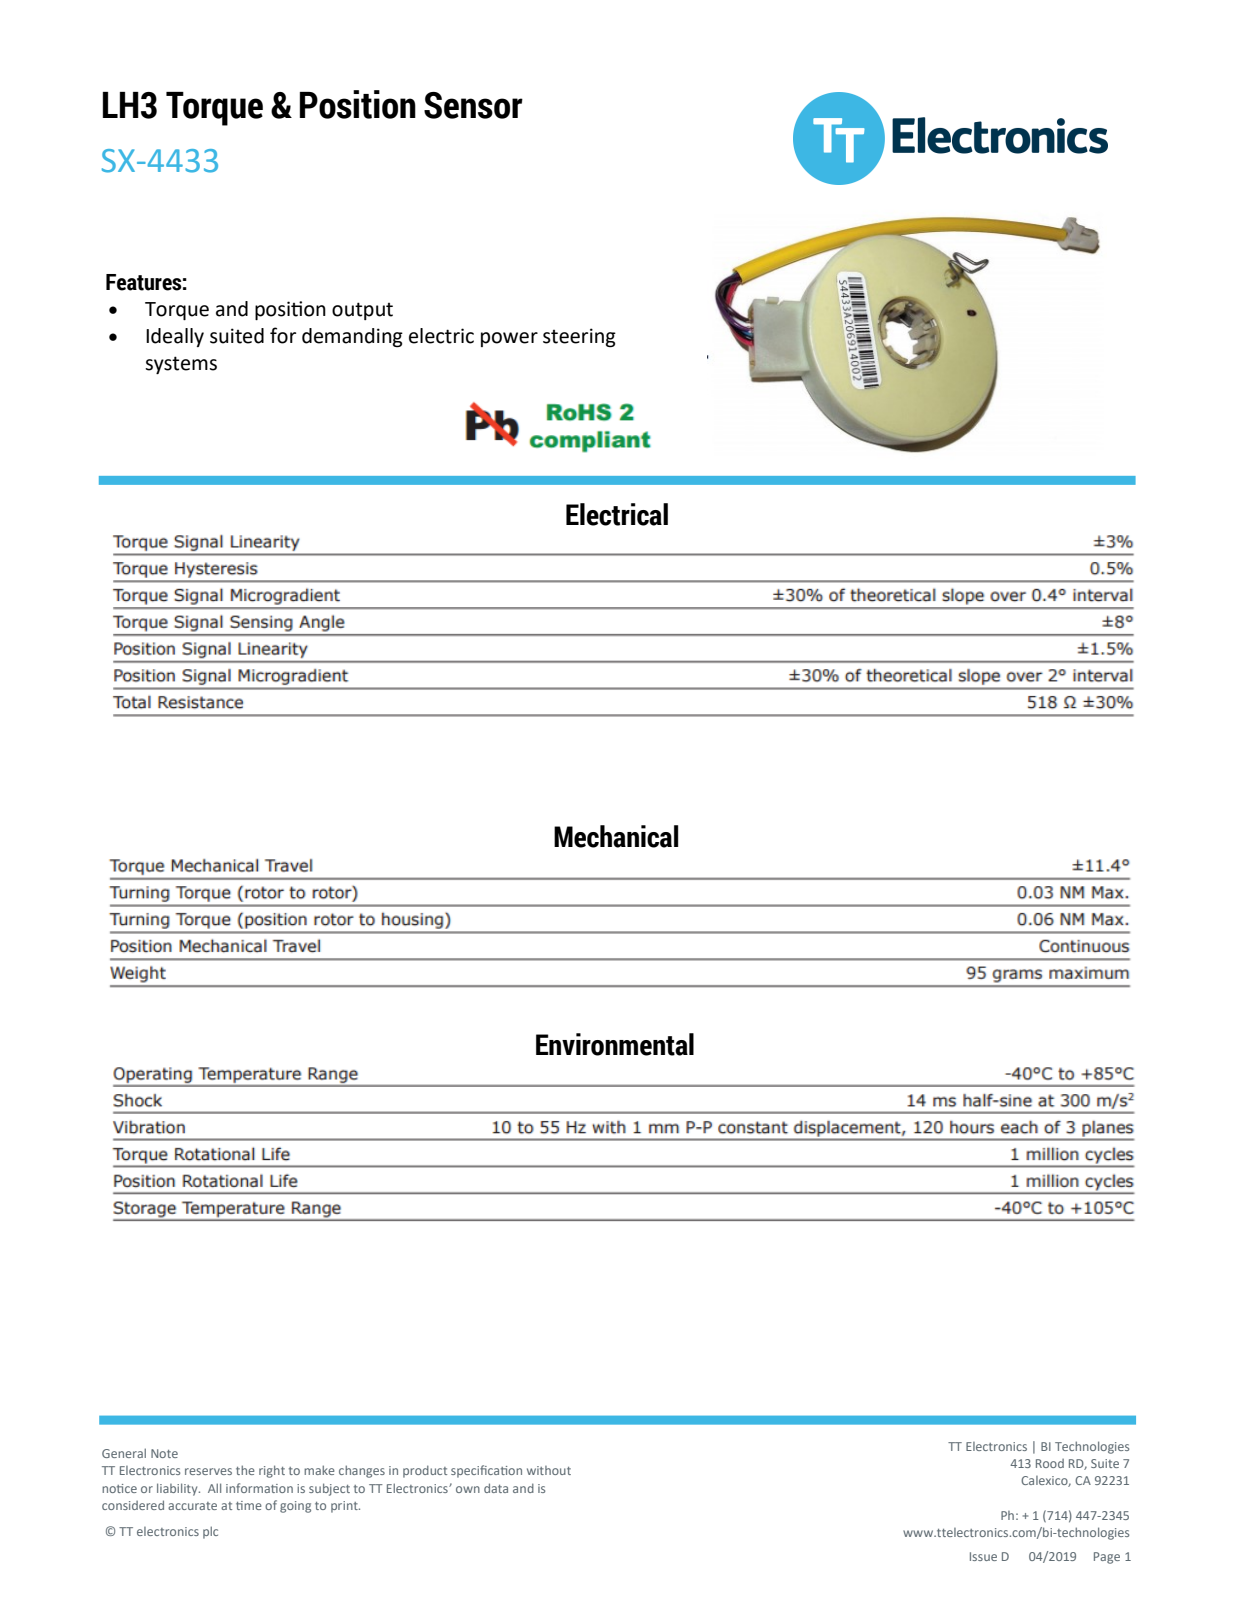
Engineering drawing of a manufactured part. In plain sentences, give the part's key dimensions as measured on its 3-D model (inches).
The part is named "SX-4433A_SW0001". Its 3-D file was written by "PRO/ENGINEER BY PARAMETRIC TECHNOLOGY CORPORATION, 2011490 (CONFIG_CONTROL_DESIGN)". It is 14 solids with 1854 faces: 855 planar, 660 cylindrical and 339 other. Overall it measures 8.597 by 3.2 by 1.728 inches. Its volume is 5.393 cubic inches and its surface area 49.76 square inches. Round holes: 6 of diameter 0.042, 4 of diameter 0.039, 1 of diameter 0.049, 1 of diameter 0.29, 1 of diameter 0.985, 1 of diameter 1.046, 1 of diameter 1.126, 1 of diameter 1.146, 1 of diameter 1.2, 1 of diameter 1.255, 1 of diameter 3.15. Round bosses or shafts: 23 of diameter 0.04, 6 of diameter 0.047, 1 of diameter 3.2, 1 of diameter 3.142, 1 of diameter 3.1, 1 of diameter 3.056, 1 of diameter 1.345, 1 of diameter 1.234. Partial cylindrical surfaces (rounded edges, fillets, slot ends): 72 of radius 0.007, 72 of radius 0.012, 63 of radius 0.01, 44 of radius 0.005, 32 of radius 0.01, 21 of radius 0.02, 19 of radius 0.016, 18 of radius 0.006. The main face-to-face distances are 0.719, 0.087, 0.521, 0.108, 0.012, 0.065, 0.729, 0.531, 0.11, 0.173. The hole center spacings are 0.115, 0.23, 0.345, 0.46, 0.575, 0.23, 0.345, 0.69.
